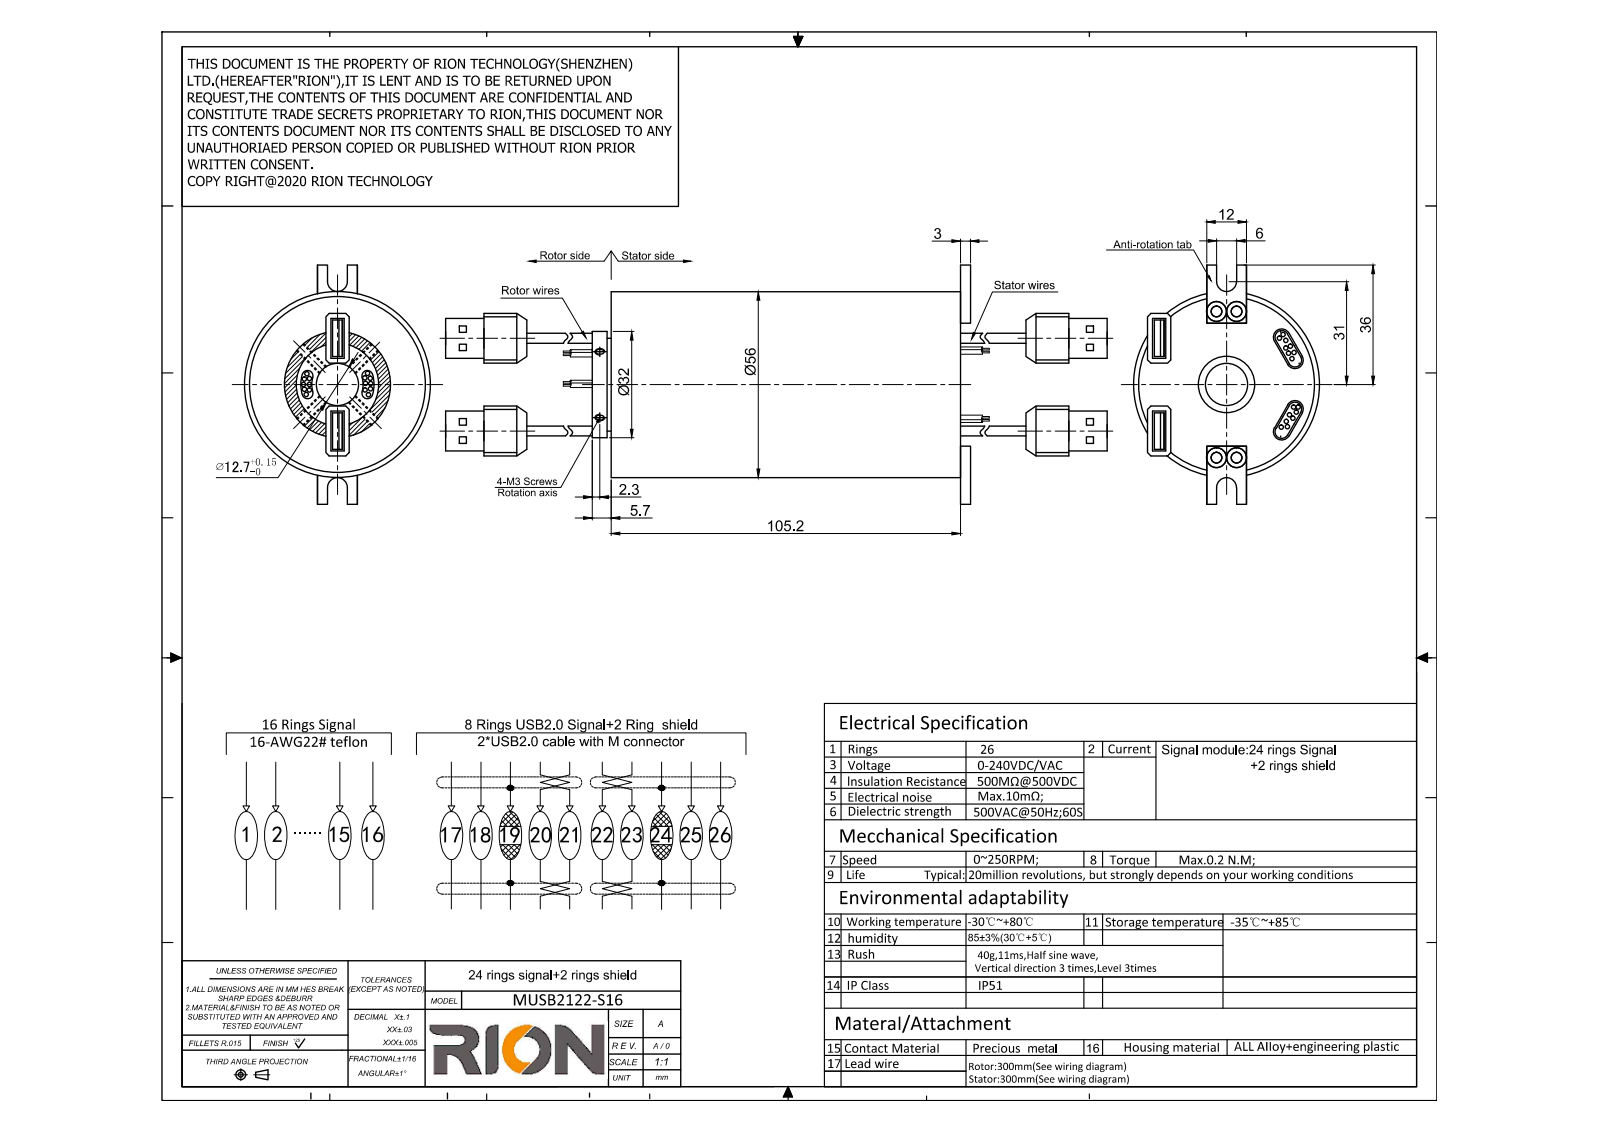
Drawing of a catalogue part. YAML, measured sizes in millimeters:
part_name: "RUSB2122-S16"
step_written_by: "SolidWorks 2014 (CONFIG_CONTROL_DESIGN)"
units: millimeters
bodies: {solids: 1, faces: 264, planar: 106, cylindrical: 142, other: 16}
overall_size: [129.4, 72, 56]
volume: 250836
surface_area: 32393
round_holes:
  - {diameter: 2.5, count: 6}
  - {diameter: 3.2, count: 4}
  - {diameter: 12.7, count: 1}
  - {diameter: 15.8, count: 1}
  - {diameter: 53, count: 1}
round_bosses_or_shafts:
  - {diameter: 1.3, count: 32}
  - {diameter: 56, count: 1}
  - {diameter: 52.9, count: 1}
  - {diameter: 52.8, count: 1}
  - {diameter: 32, count: 1}
  - {diameter: 15.5, count: 1}
partial_cylinders:
  - {radius: 2, count: 16}
  - {radius: 3, count: 2}
  - {radius: 7.5, count: 1}
  - {radius: 11.5, count: 1}
face_to_face_distances: [105.2, 5.7, 110.9, 3, 10, 1, 113.9, 108.2, 4, 104.2]
hole_center_spacings: [22.7, 6, 45, 45.4]
